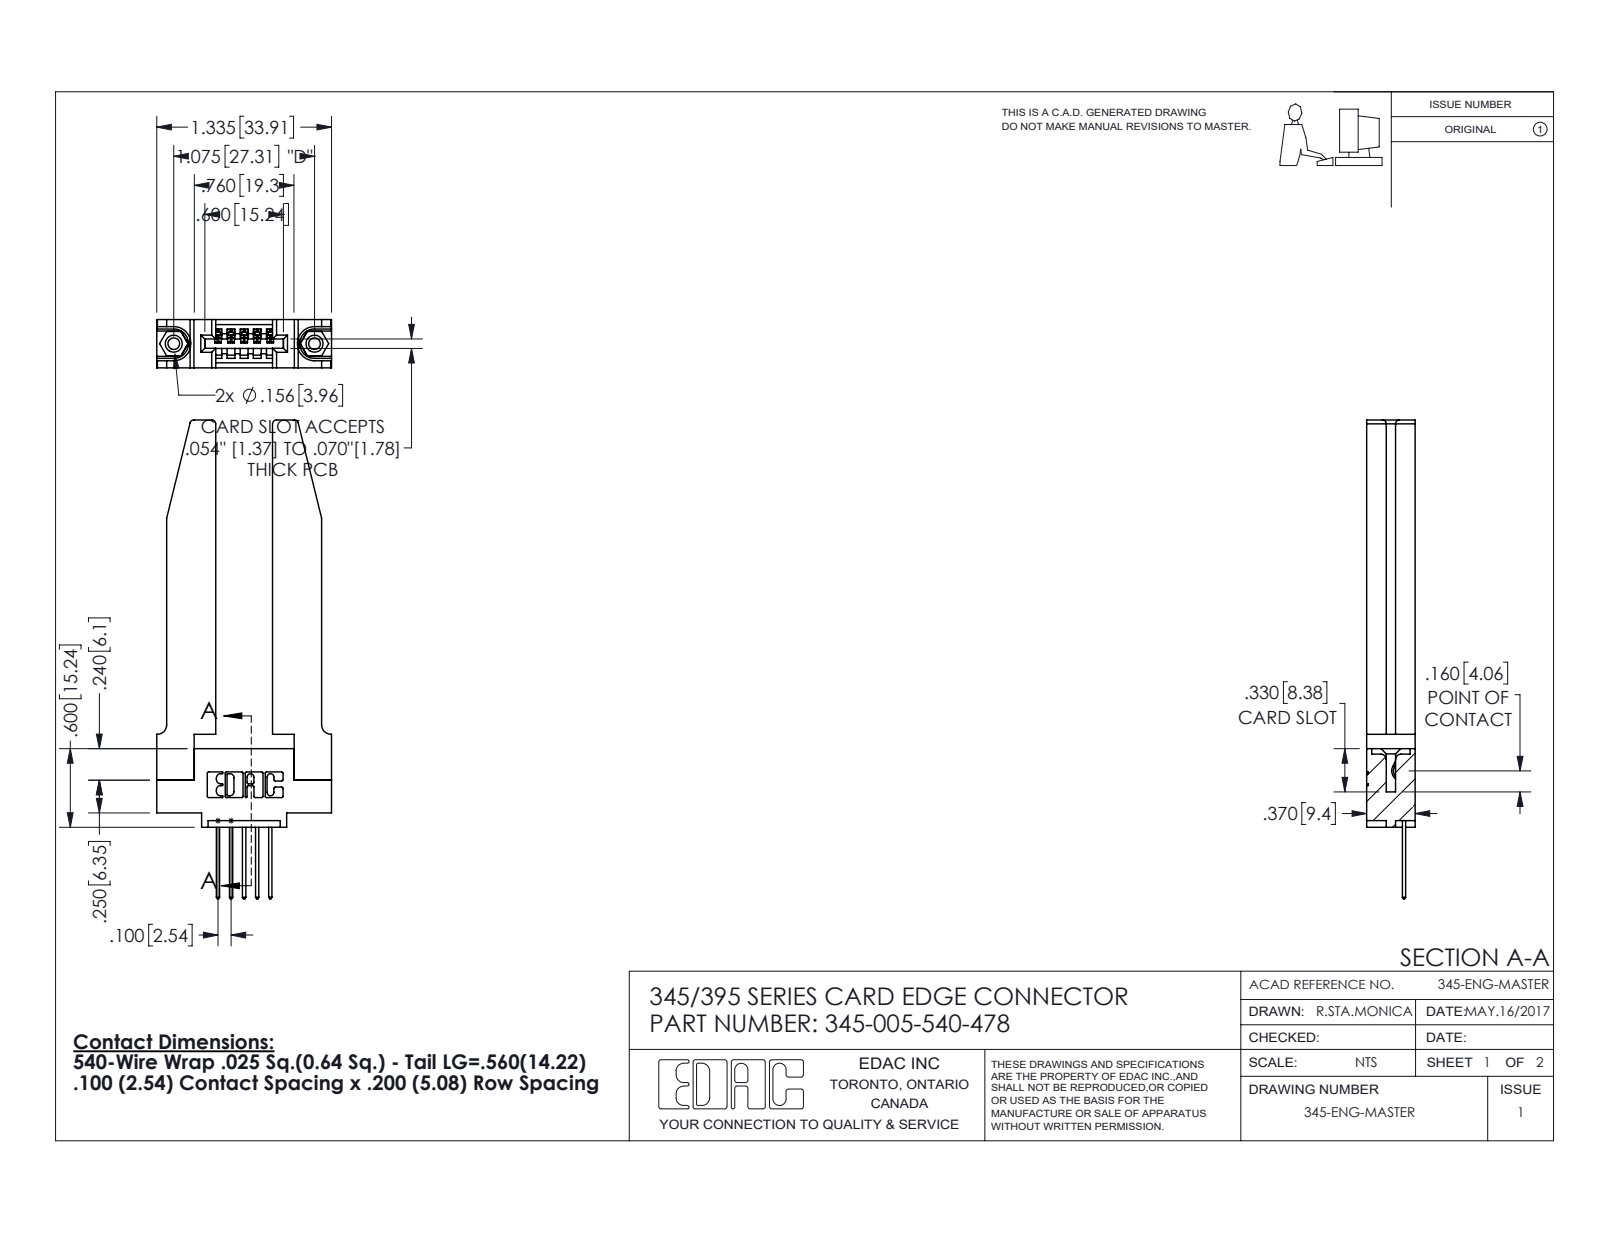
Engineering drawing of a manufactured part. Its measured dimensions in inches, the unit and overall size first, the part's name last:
Units: inches
Overall size (bounding box): 3.657 × 1.336 × 0.37
Round holes (diameter × count): ⌀0.089 ×2, ⌀0.125 ×2, ⌀0.156 ×2, ⌀0.064 ×1
Round bosses / shafts (diameter × count): ⌀0.155 ×2
Partial cylindrical surfaces — rounded edges, fillets, slot ends (radius × count): R0.01 ×22, R0.006 ×10, R0.01 ×10, R0.03 ×8, R0.007 ×6, R0.031 ×6, R0.026 ×3, R0.031 ×2
Main face-to-face distances: 0.37, 0.15, 0.22, 0.435, 0.072, 0.148, 0.298, 0.077, 0.2, 0.071
Hole centre spacings: 0.27, 0.847, 1.075
Volume: 0.648 in³ · Surface area: 15.91 in²
Bodies: 10 solids, 654 faces (426 planar, 176 cylindrical, 52 other)
Part name (STEP PRODUCT): 345-250-001_345-250-001-102; 345-292-001_345-293-140; 345-220-078_345-220-078; 345 Part_0.110 Offset - 0.156 Dia-TH (+1 more)
STEP written by: SolidWorks 2016 (CONFIG_CONTROL_DESIGN)
